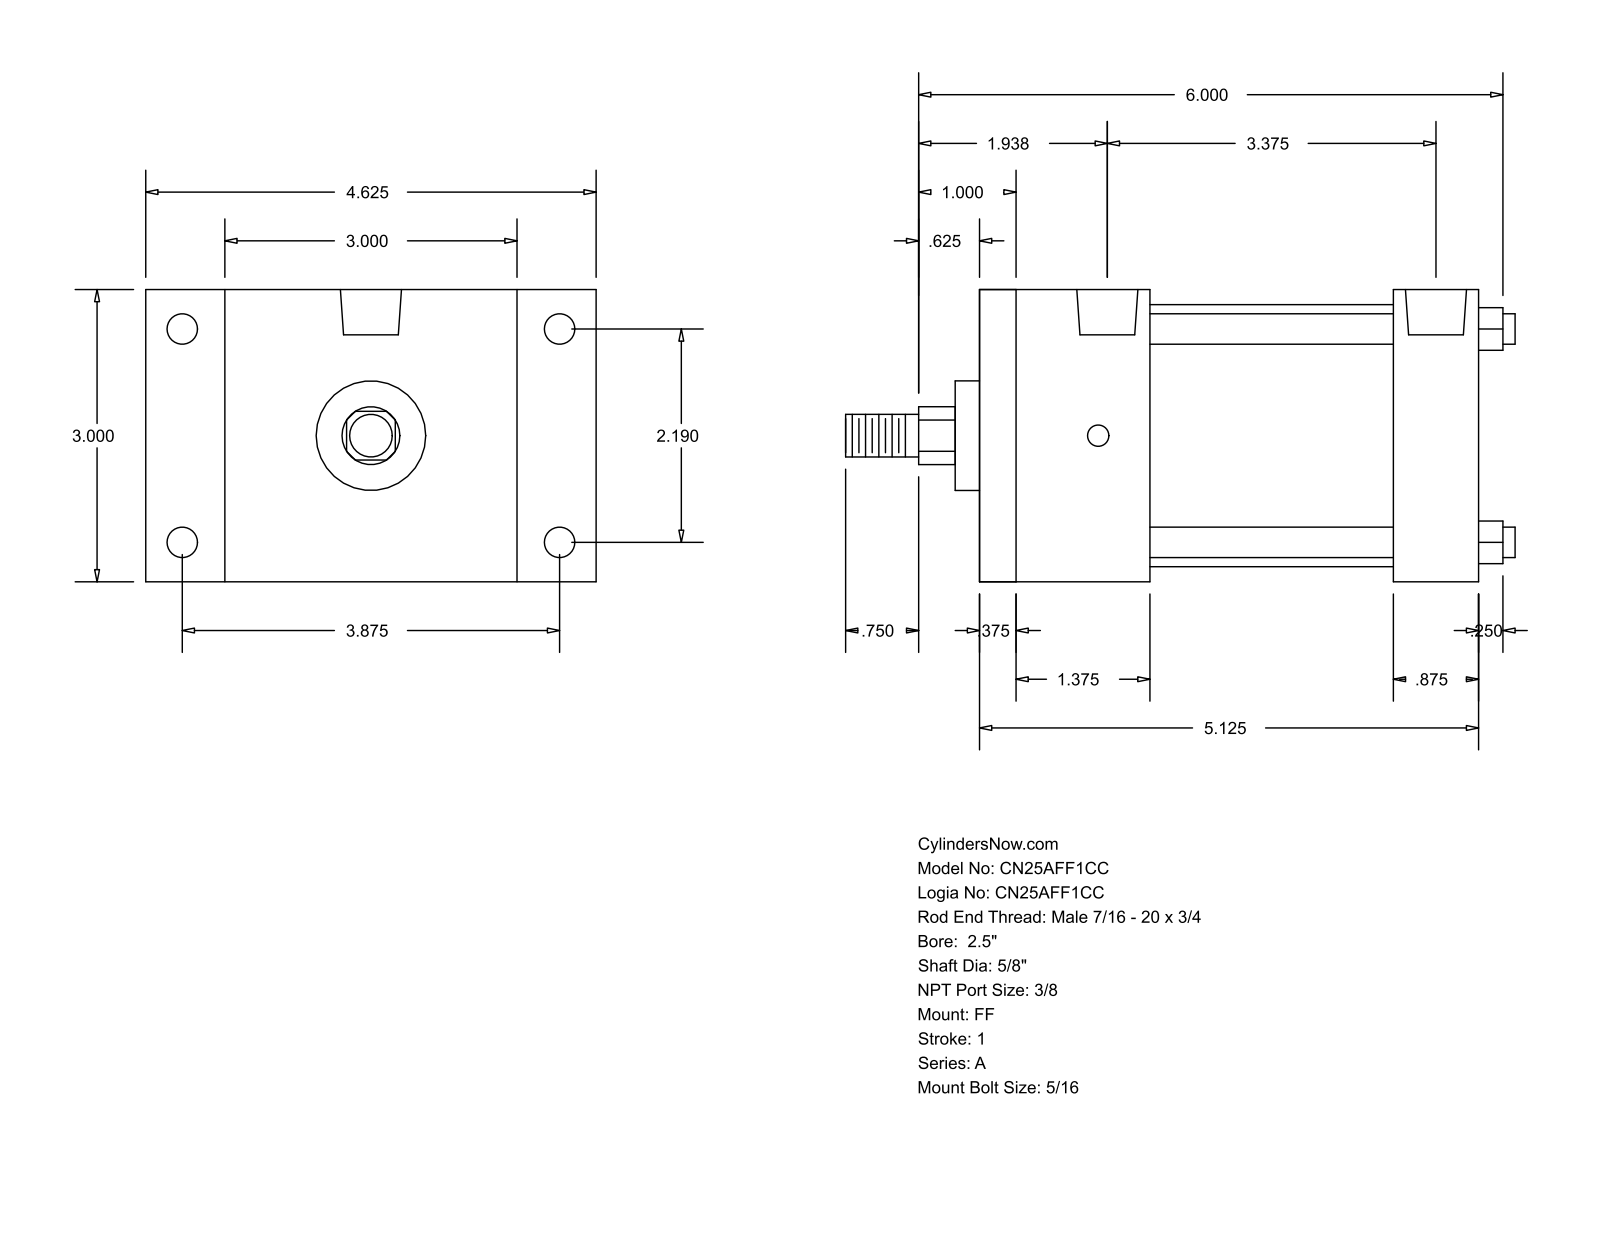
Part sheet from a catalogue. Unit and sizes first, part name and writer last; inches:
Units: inches
Overall size (bounding box): 6.875 × 4.625 × 3
Round holes (diameter × count): ⌀0.219 ×4, ⌀0.313 ×4, ⌀0.627 ×2
Round bosses / shafts (diameter × count): ⌀0.313 ×4, ⌀2.69 ×1, ⌀1.125 ×1, ⌀0.625 ×1, ⌀0.437 ×1
Partial cylindrical surfaces — rounded edges, fillets, slot ends (radius × count): R0.297 ×1
Main face-to-face distances: 3, 5.125, 0.375, 4.75, 1.75, 1.375, 4.25, 3.875, 2.5, 3.375
Hole centre spacings: 0.094, 2.19, 3.469, 3.563, 3.875, 4.451, 3.375
Bodies: 0 solids, 92 faces (64 planar, 28 cylindrical, 0 other)
Part name (STEP PRODUCT): A_FF__0250_0.625
STEP written by: GSSL Pune (CONFIG_CONTROL_DESIGN)
